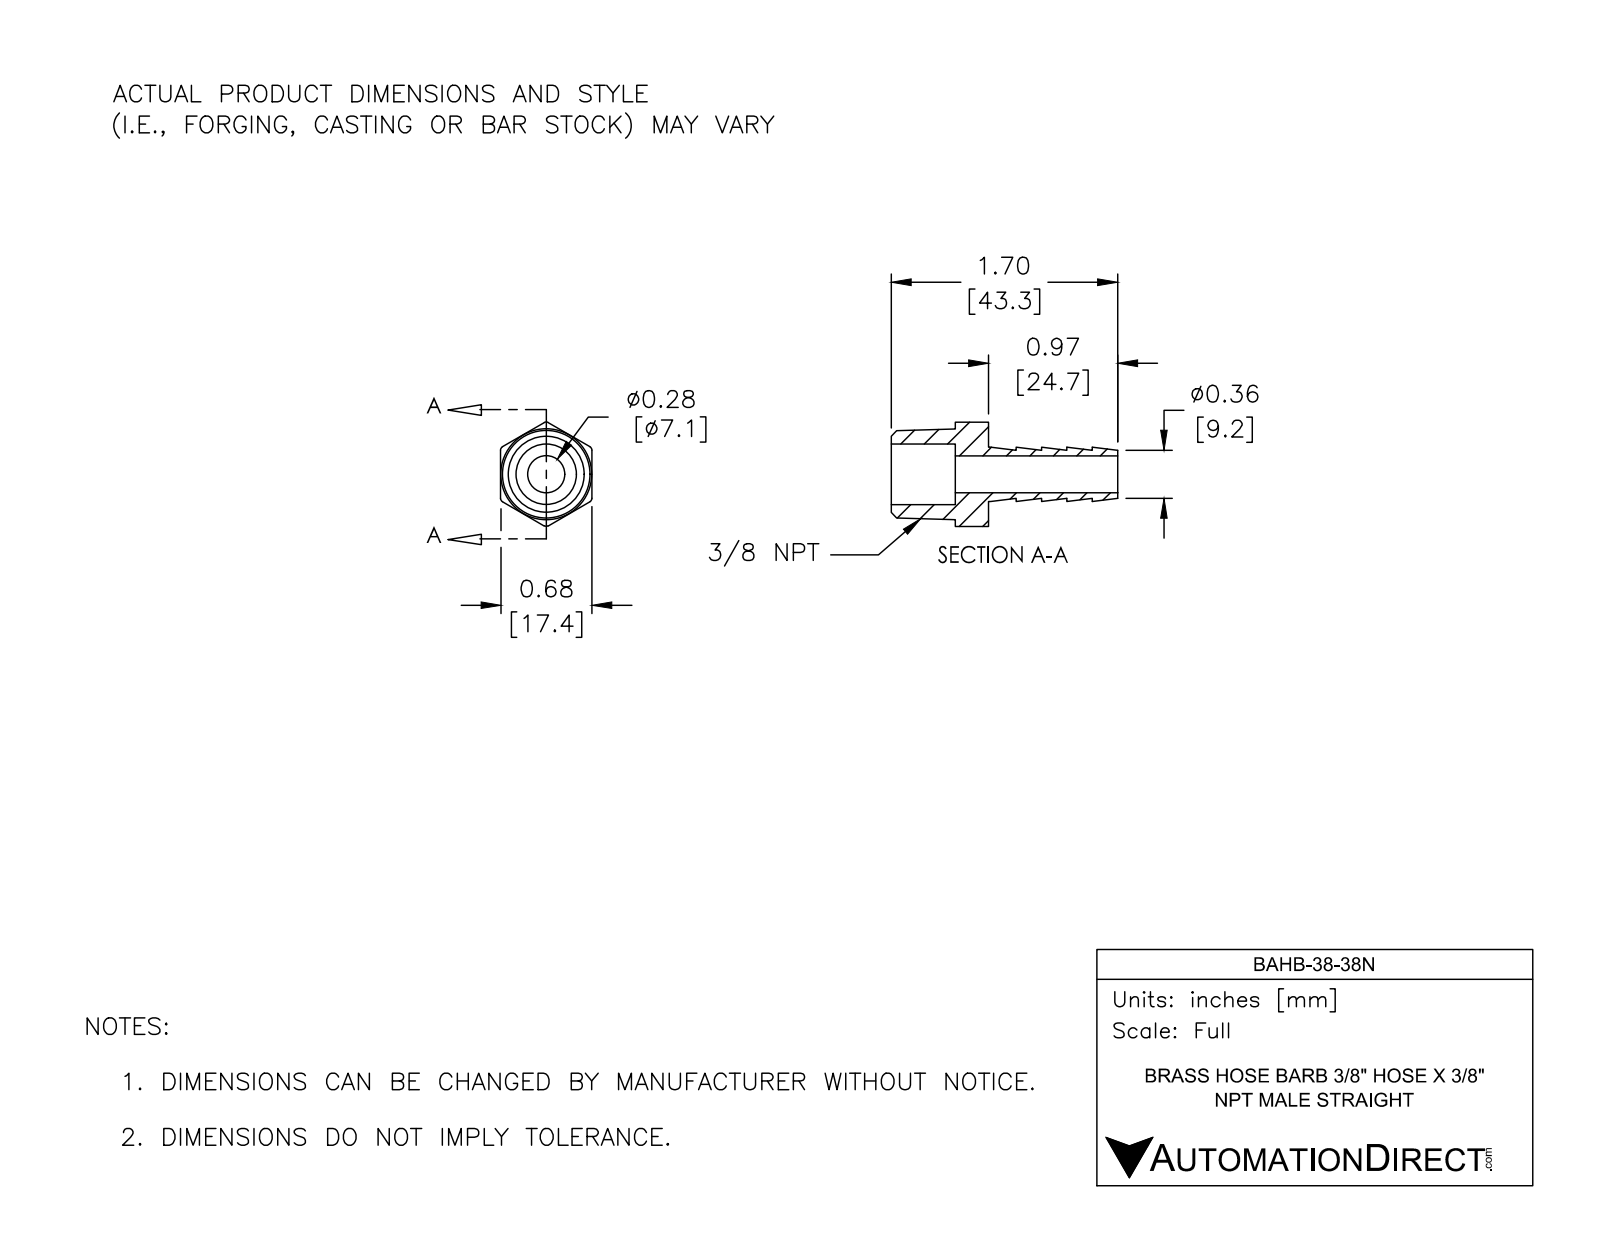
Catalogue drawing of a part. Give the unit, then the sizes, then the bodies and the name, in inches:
Units: inches
Overall size (bounding box): 1.703 × 0.785 × 0.687
Round holes (diameter × count): ⌀0.278 ×1, ⌀0.455 ×1
Round bosses / shafts (diameter × count): ⌀0.408 ×1
Partial cylindrical surfaces — rounded edges, fillets, slot ends (radius × count): R0.03 ×6
Main face-to-face distances: 0.687, 0.25, 0.191, 0.731, 0.481, 0.382, 0.573, 0.972, 1.222, 1.703
Volume: 0.231 in³ · Surface area: 5.242 in²
Bodies: 1 solid, 41 faces (15 planar, 12 cylindrical, 14 other)
Part name (STEP PRODUCT): BAHB-38-38N
STEP written by: SolidWorks 2017 (AUTOMOTIVE_DESIGN)
